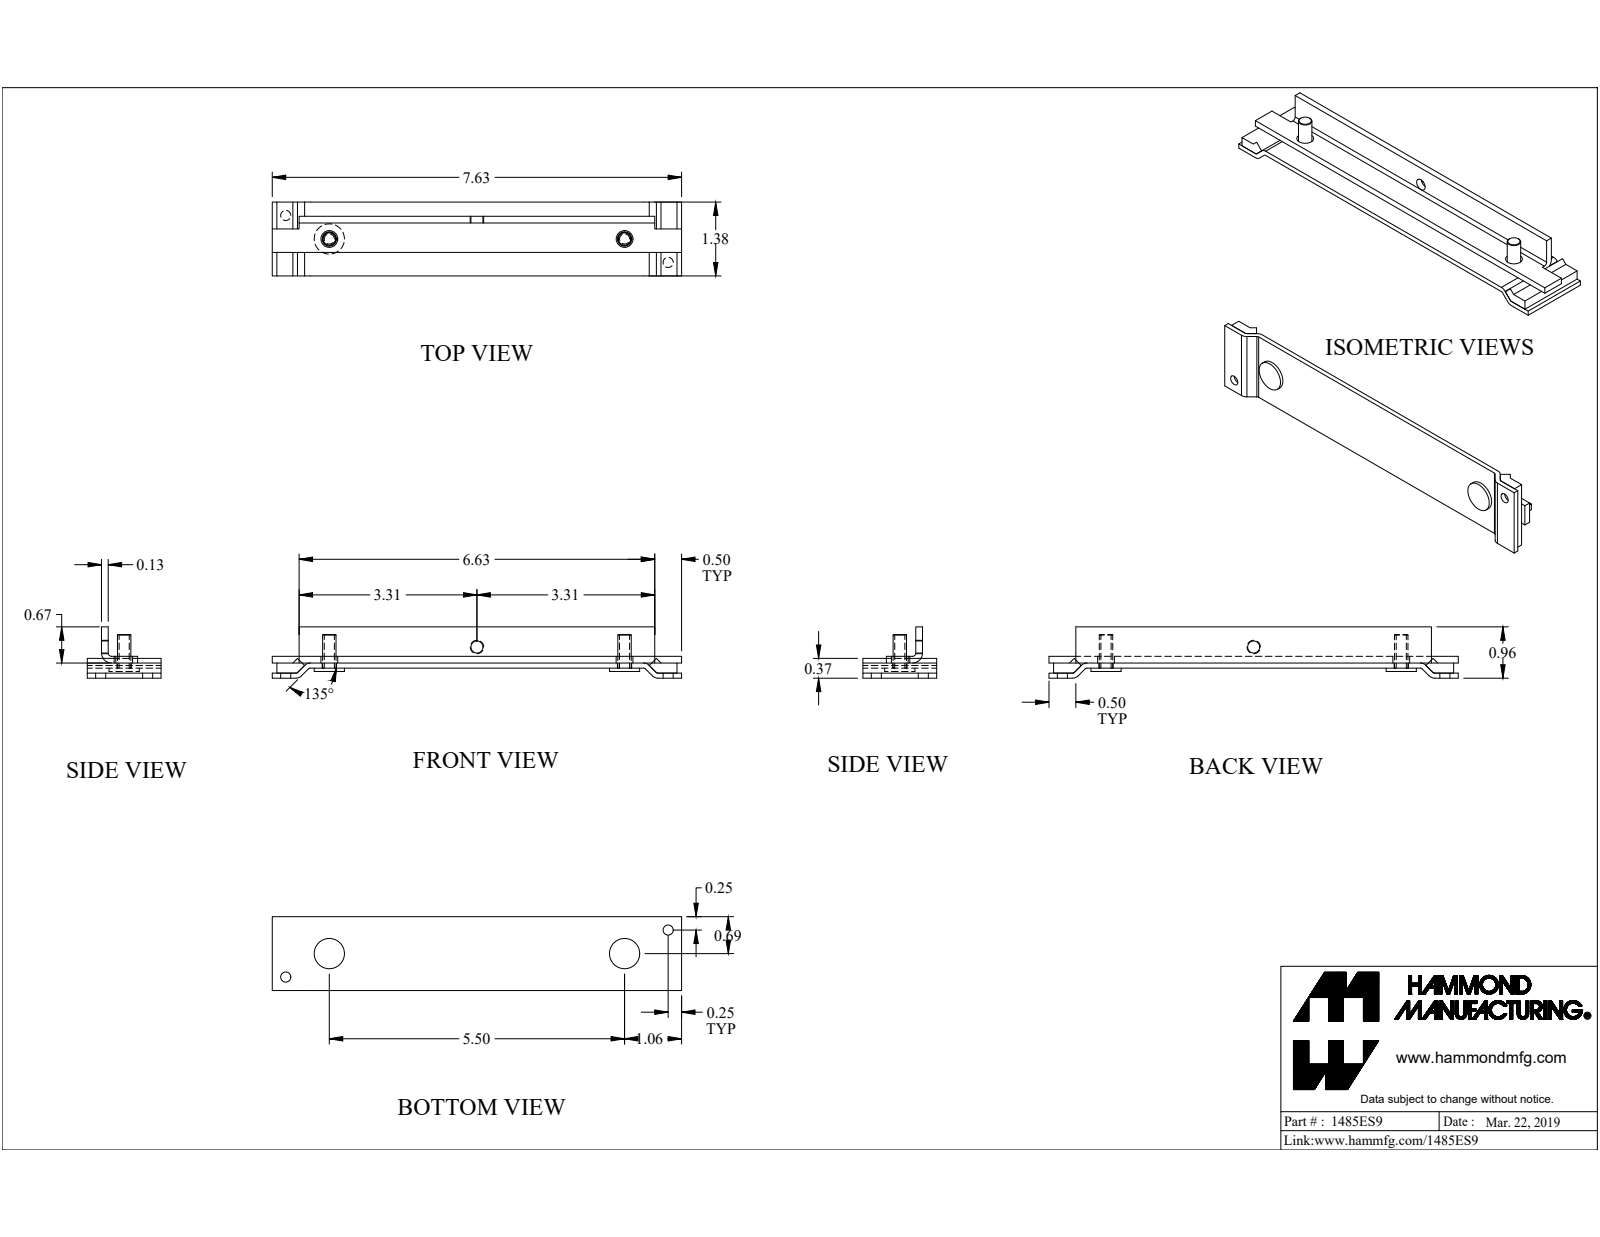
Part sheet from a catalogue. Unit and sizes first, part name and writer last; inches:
Units: inches
Overall size (bounding box): 7.625 × 1.375 × 0.956
Round holes (diameter × count): ⌀0.187 ×2, ⌀0.265 ×2, ⌀0.313 ×2, ⌀0.224 ×1
Round bosses / shafts (diameter × count): ⌀0.563 ×2, ⌀0.25 ×2
Partial cylindrical surfaces — rounded edges, fillets, slot ends (radius × count): R0.048 ×4, R0.143 ×4, R0.06 ×1, R0.185 ×1
Main face-to-face distances: 0.095, 0.125, 0.22, 0.093, 0.188, 0.313, 0.673, 0.548, 0.095, 0.187
Hole centre spacings: 0.923, 6.328, 5.5, 7.179
Volume: 2.345 in³ · Surface area: 47.85 in²
Bodies: 6 solids, 71 faces (48 planar, 21 cylindrical, 2 other)
Part name (STEP PRODUCT): 1485ES9
STEP written by: SolidWorks 2019 (CONFIG_CONTROL_DESIGN)
